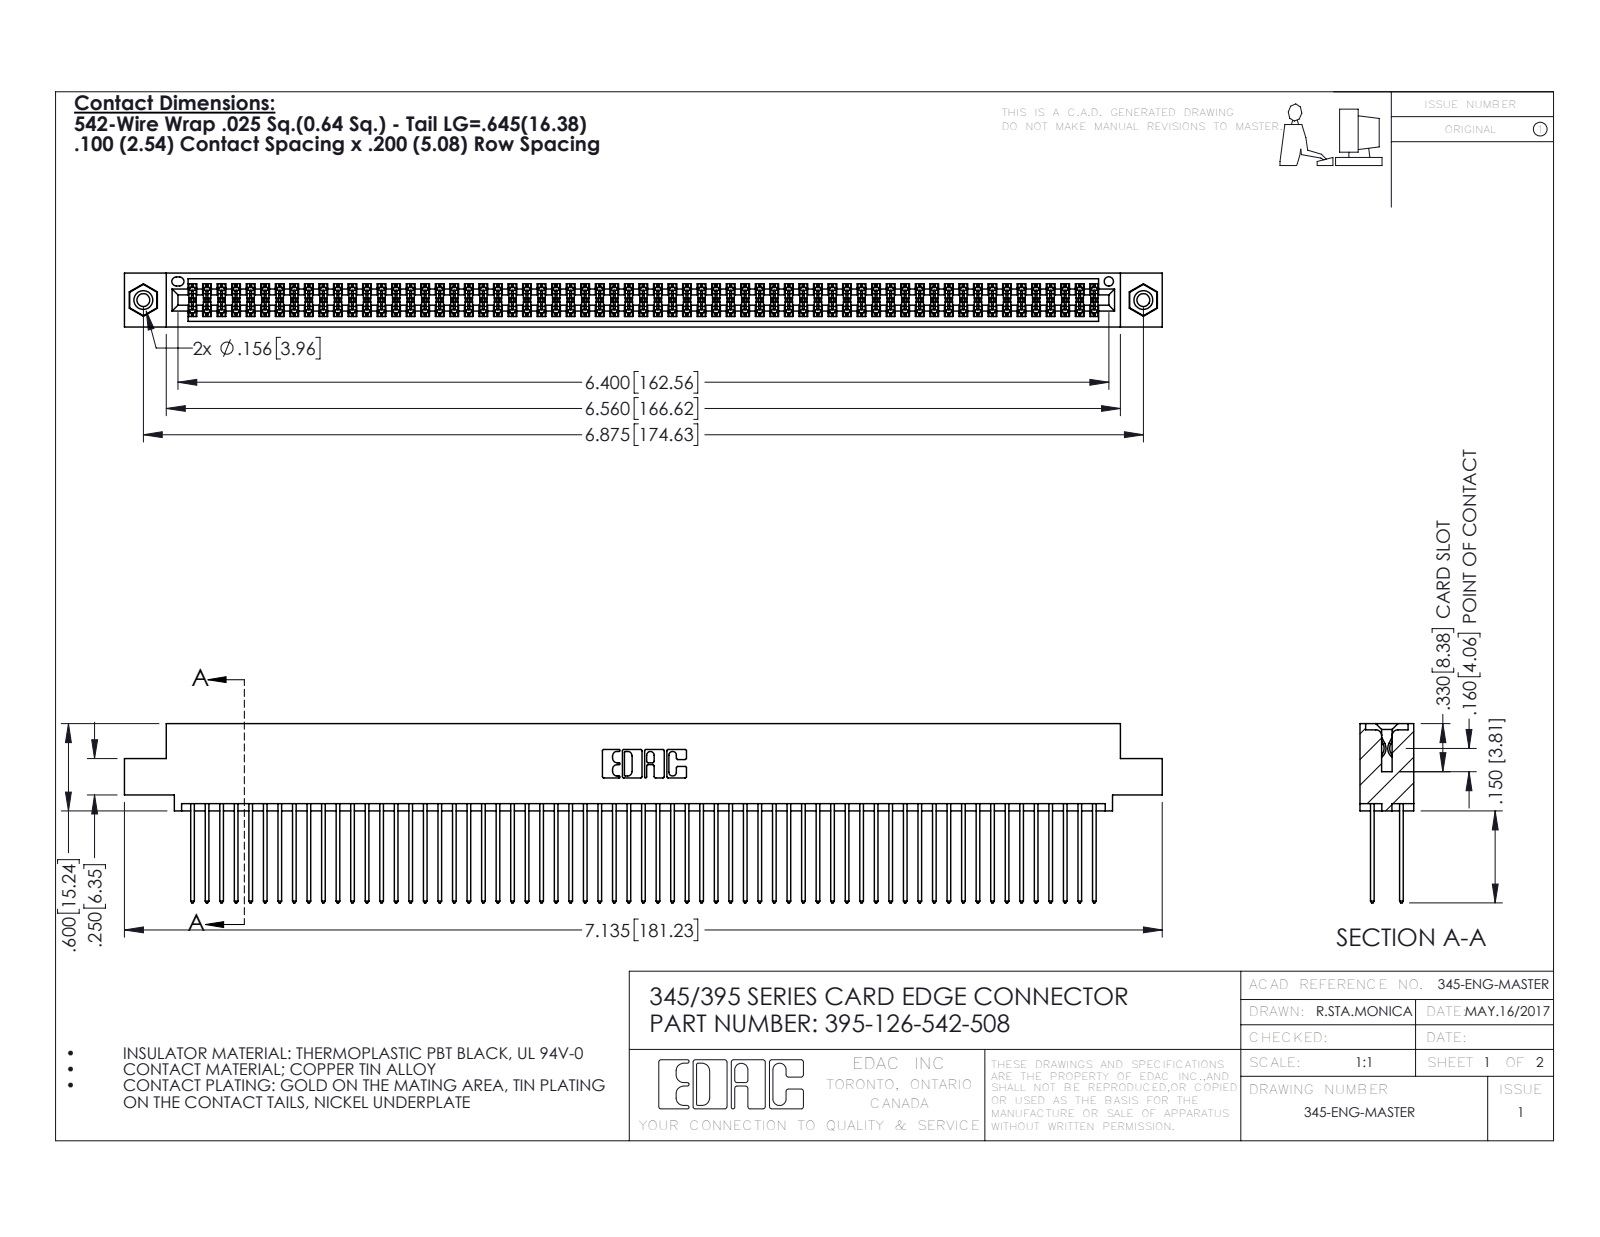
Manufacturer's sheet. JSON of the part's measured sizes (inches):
{"part_name": "345 Part_0.110 Offset - 0.156 Dia-TI; 345-250-001_345-250-003-102; 345-292-001_345-293-142; 395-126-542-508", "step_written_by": "SolidWorks 2016 (CONFIG_CONTROL_DESIGN)", "units": "inches", "bodies": {"solids": 129, "faces": 6490, "planar": 4274, "cylindrical": 2200, "other": 16}, "overall_size": [7.135, 1.232, 0.37], "volume_in3": 1.117, "surface_area_in2": 46.99, "round_holes": [[0.089, 2], [0.125, 2], [0.156, 2], [0.064, 1]], "round_bosses_or_shafts": [[0.155, 2]], "partial_cylinders_radius": [[0.006, 189], [0.01, 126], [0.01, 22], [0.007, 6], [0.031, 6], [0.026, 3], [0.014, 2], [0.019, 2]], "face_to_face_distances": [0.072, 0.298, 0.2, 0.098, 0.272, 0.025, 0.225, 0.37, 0.175, 0.149], "hole_center_spacings": [0.27, 6.639, 6.875]}
